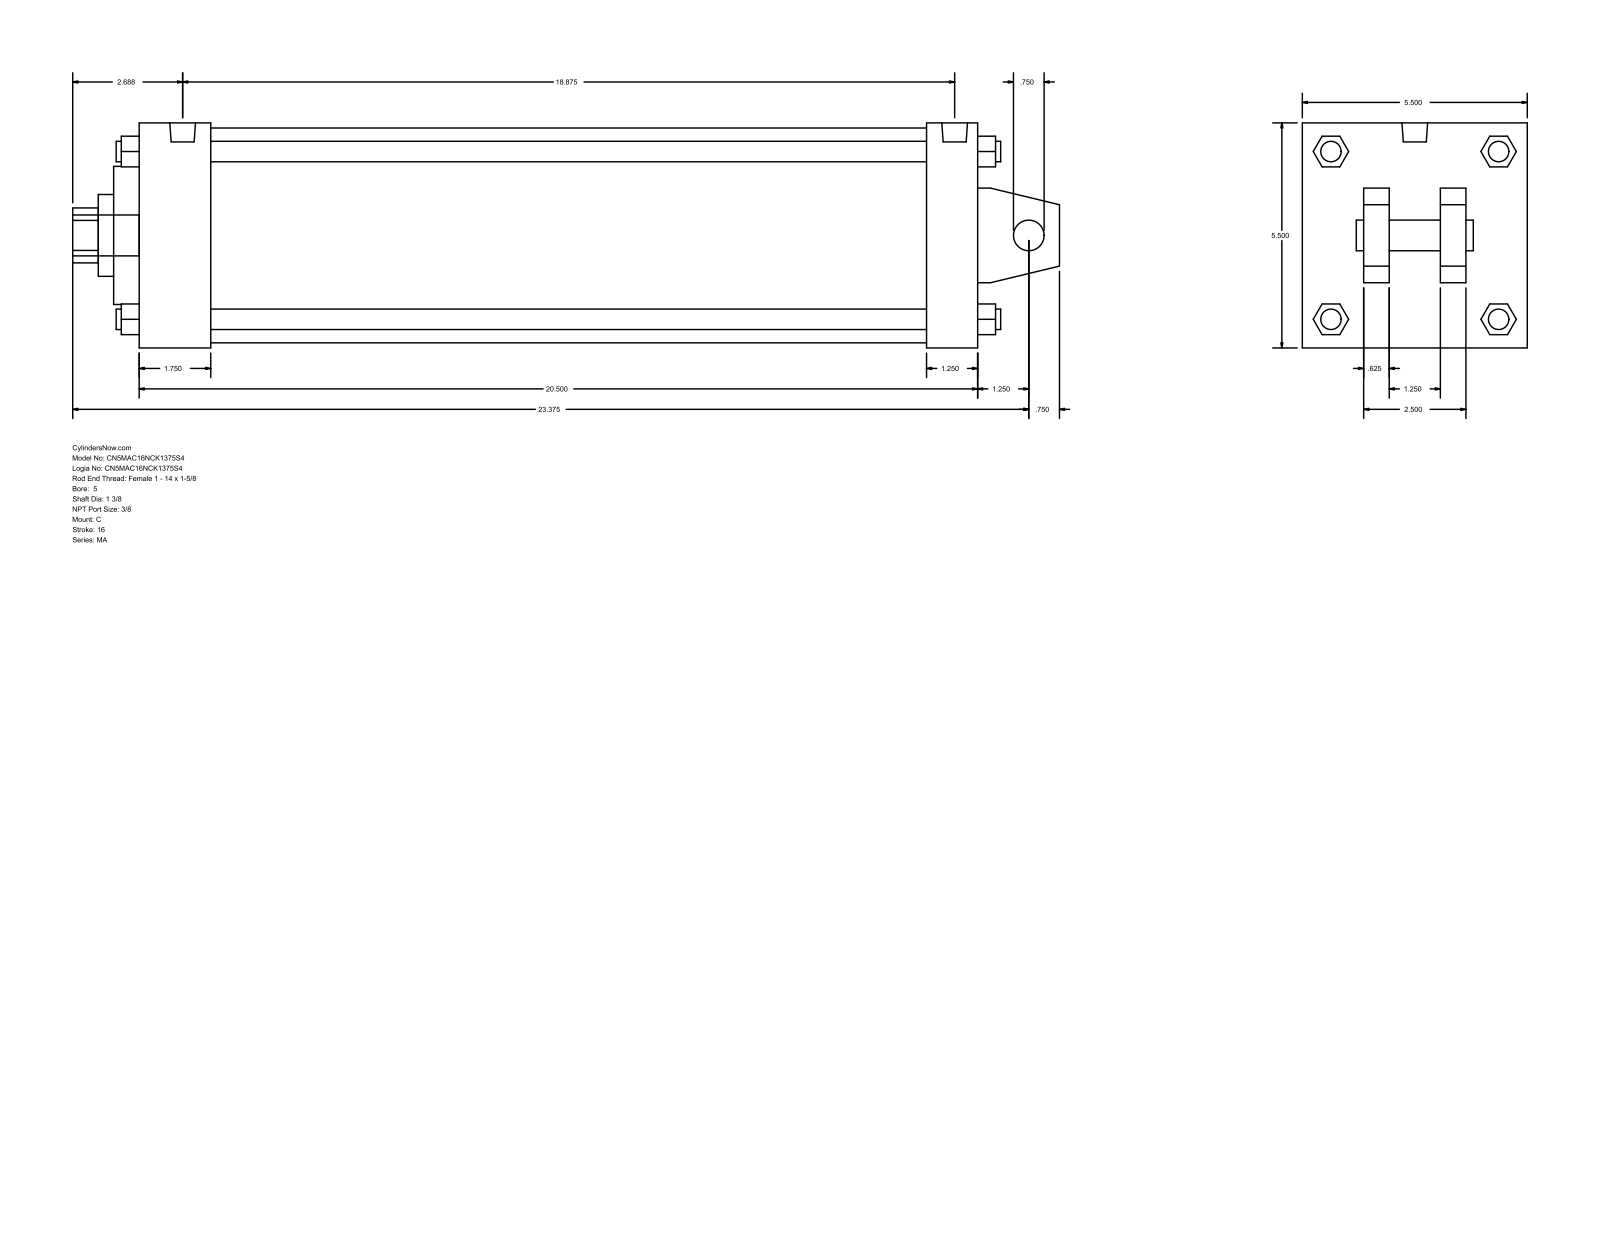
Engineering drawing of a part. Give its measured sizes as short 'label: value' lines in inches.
name: MA_C__0500_1.375
written by: GSSL Pune (CONFIG_CONTROL_DESIGN)
unit: in
bodies: 0 solids, 141 faces (109 planar, 32 cylindrical, 0 other)
size: 24.125 × 5.5 × 5.5
holes: 1× ⌀0.75, 1× ⌀1.375, 1× ⌀2, 1× ⌀3.375, 1× ⌀5.25
bosses: 4× ⌀0.5, 4× ⌀0.437, 2× ⌀0.627, 1× ⌀1
rounds: 1× R0.672
face distances: 5.5, 20.5, 0.625, 19.25, 1.25, 1.75, 17.5, 18.75, 1.5, 4
